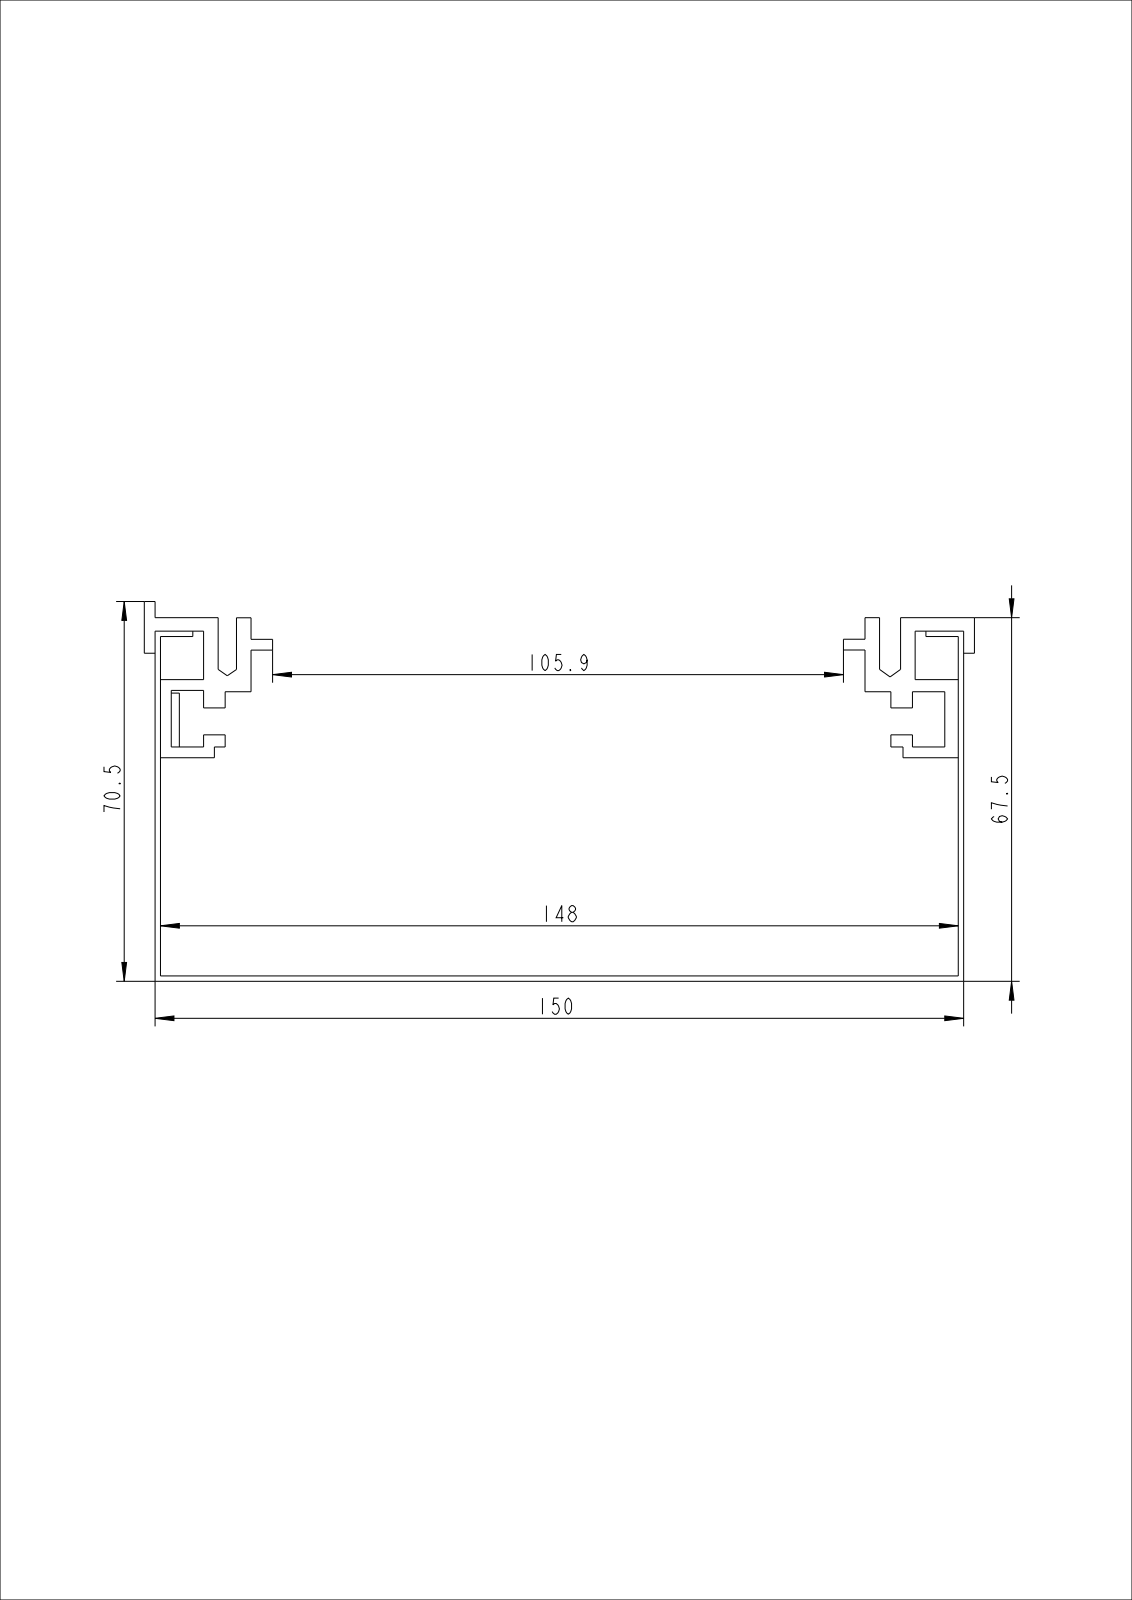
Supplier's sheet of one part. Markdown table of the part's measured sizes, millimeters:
| quantity | value |
| --- | --- |
| part name | AKU1500701_WANNE; AKU_SEITENPROFIL_APA_K24; ZES_VK180_KUN; AKU_SEITENPROFIL_APA_O01 (+1 more) |
| STEP written by | CREO PARAMETRIC BY PTC INC, 2022024 (AUTOMOTIVE_DESIGN) |
| units | millimeters |
| bodies | 9 solids, 265 faces (253 planar, 12 cylindrical, 0 other) |
| overall size | 2450 × 154 × 70.5 |
| volume | 1 341 000 mm³ |
| surface area | 1 941 000 mm² |
| round holes (diameter × count) | 5.5 × 4, 4.2 × 2 |
| main face-to-face distances | 1, 149, 148, 150, 2, 64, 8, 3, 9, 65 |
| hole center spacings | 9.25, 66.5, 18.5, 57.25, 75.75, 48, 85 |
